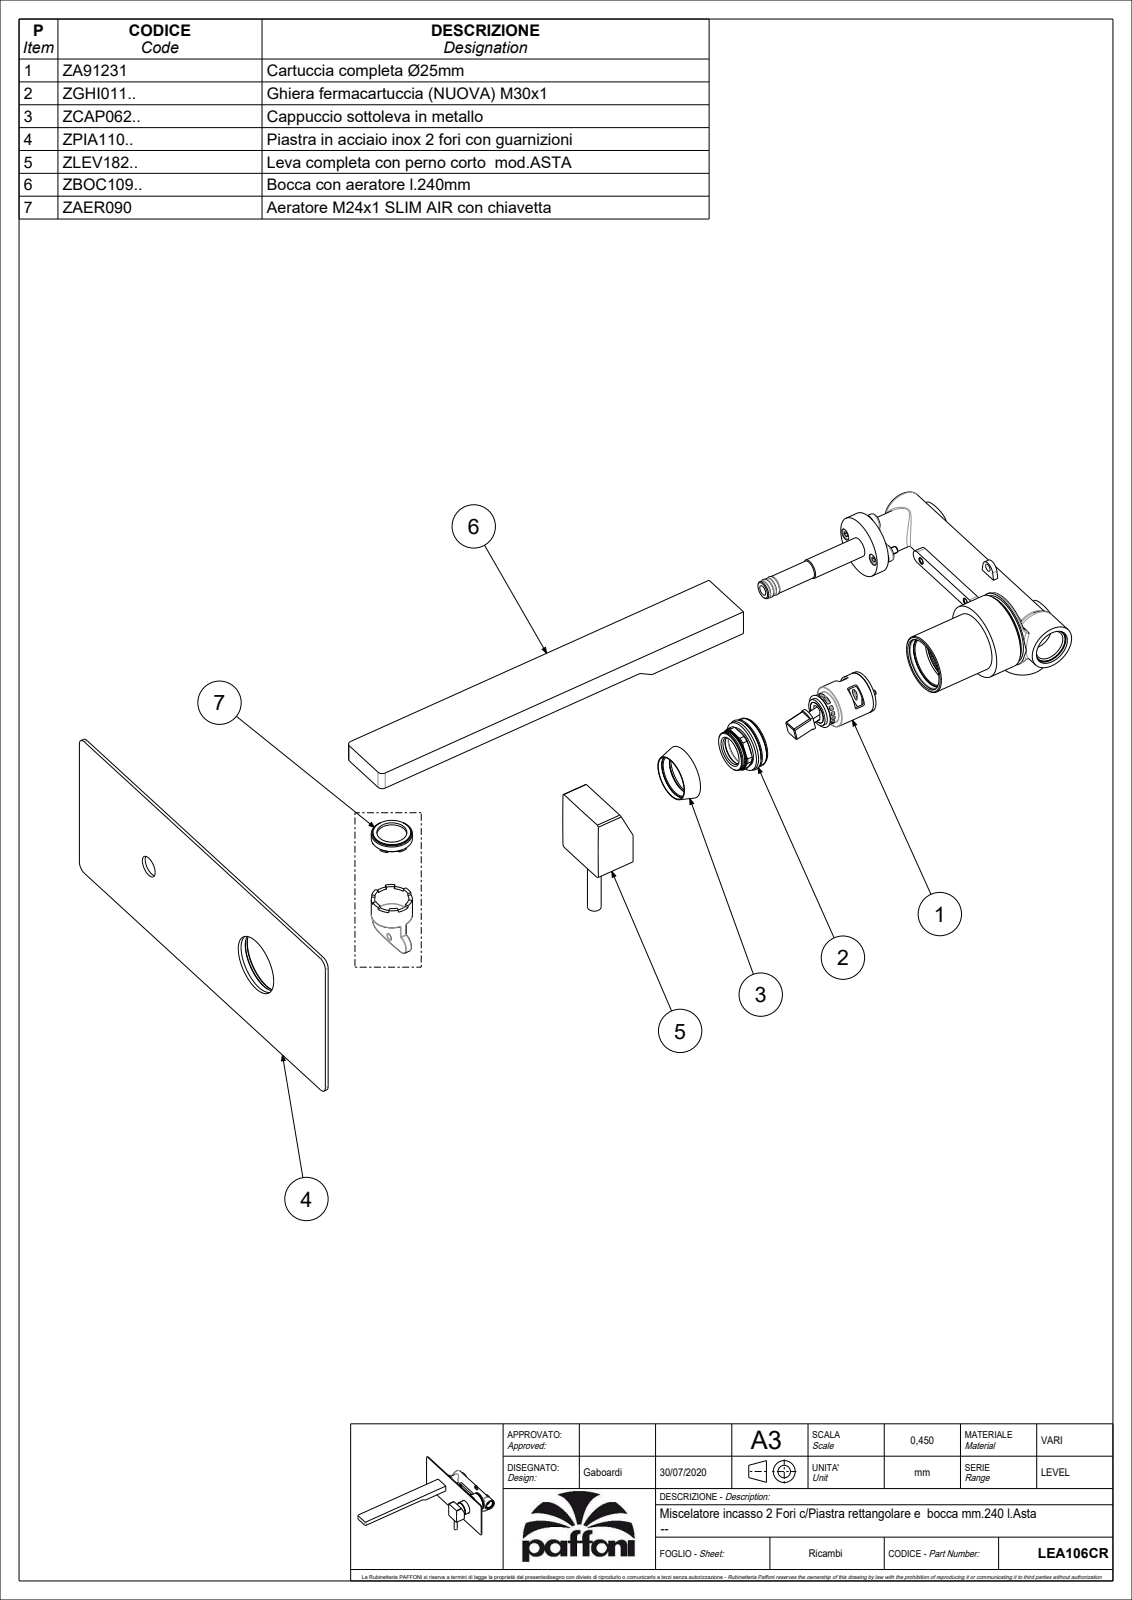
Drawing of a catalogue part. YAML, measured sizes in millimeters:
part_name: "LEA106CR"
step_written_by: "CREO PARAMETRIC BY PTC INC, 2020044 (CONFIG_CONTROL_DESIGN)"
units: millimeters
bodies: {solids: 2, faces: 677, planar: 210, cylindrical: 252, other: 215}
overall_size: [260, 250, 110.16]
volume: 189744
surface_area: 106784
round_holes:
  - {diameter: 6, count: 2}
  - {diameter: 11, count: 2}
  - {diameter: 8.2, count: 1}
  - {diameter: 12, count: 1}
  - {diameter: 13, count: 1}
  - {diameter: 15, count: 1}
  - {diameter: 16.7, count: 1}
  - {diameter: 17, count: 1}
  - {diameter: 17.5, count: 1}
  - {diameter: 19.2, count: 1}
  - {diameter: 20.2, count: 1}
  - {diameter: 22.7, count: 1}
round_bosses_or_shafts:
  - {diameter: 35.2, count: 1}
  - {diameter: 30, count: 1}
  - {diameter: 27.7, count: 1}
  - {diameter: 25, count: 1}
  - {diameter: 23.8, count: 1}
  - {diameter: 22.5, count: 1}
  - {diameter: 20, count: 1}
  - {diameter: 19, count: 1}
partial_cylinders:
  - {radius: 0.5, count: 56}
  - {radius: 1, count: 7}
  - {radius: 2, count: 4}
  - {radius: 5, count: 4}
  - {radius: 2.1, count: 3}
  - {radius: 2.5, count: 2}
  - {radius: 3, count: 2}
  - {radius: 3.5, count: 2}
face_to_face_distances: [2, 11.5, 35, 5, 16.5, 41.75, 58.25, 73.5, 108.5, 144.5]
hole_center_spacings: [1.16, 109, 109.01, 232.78]
